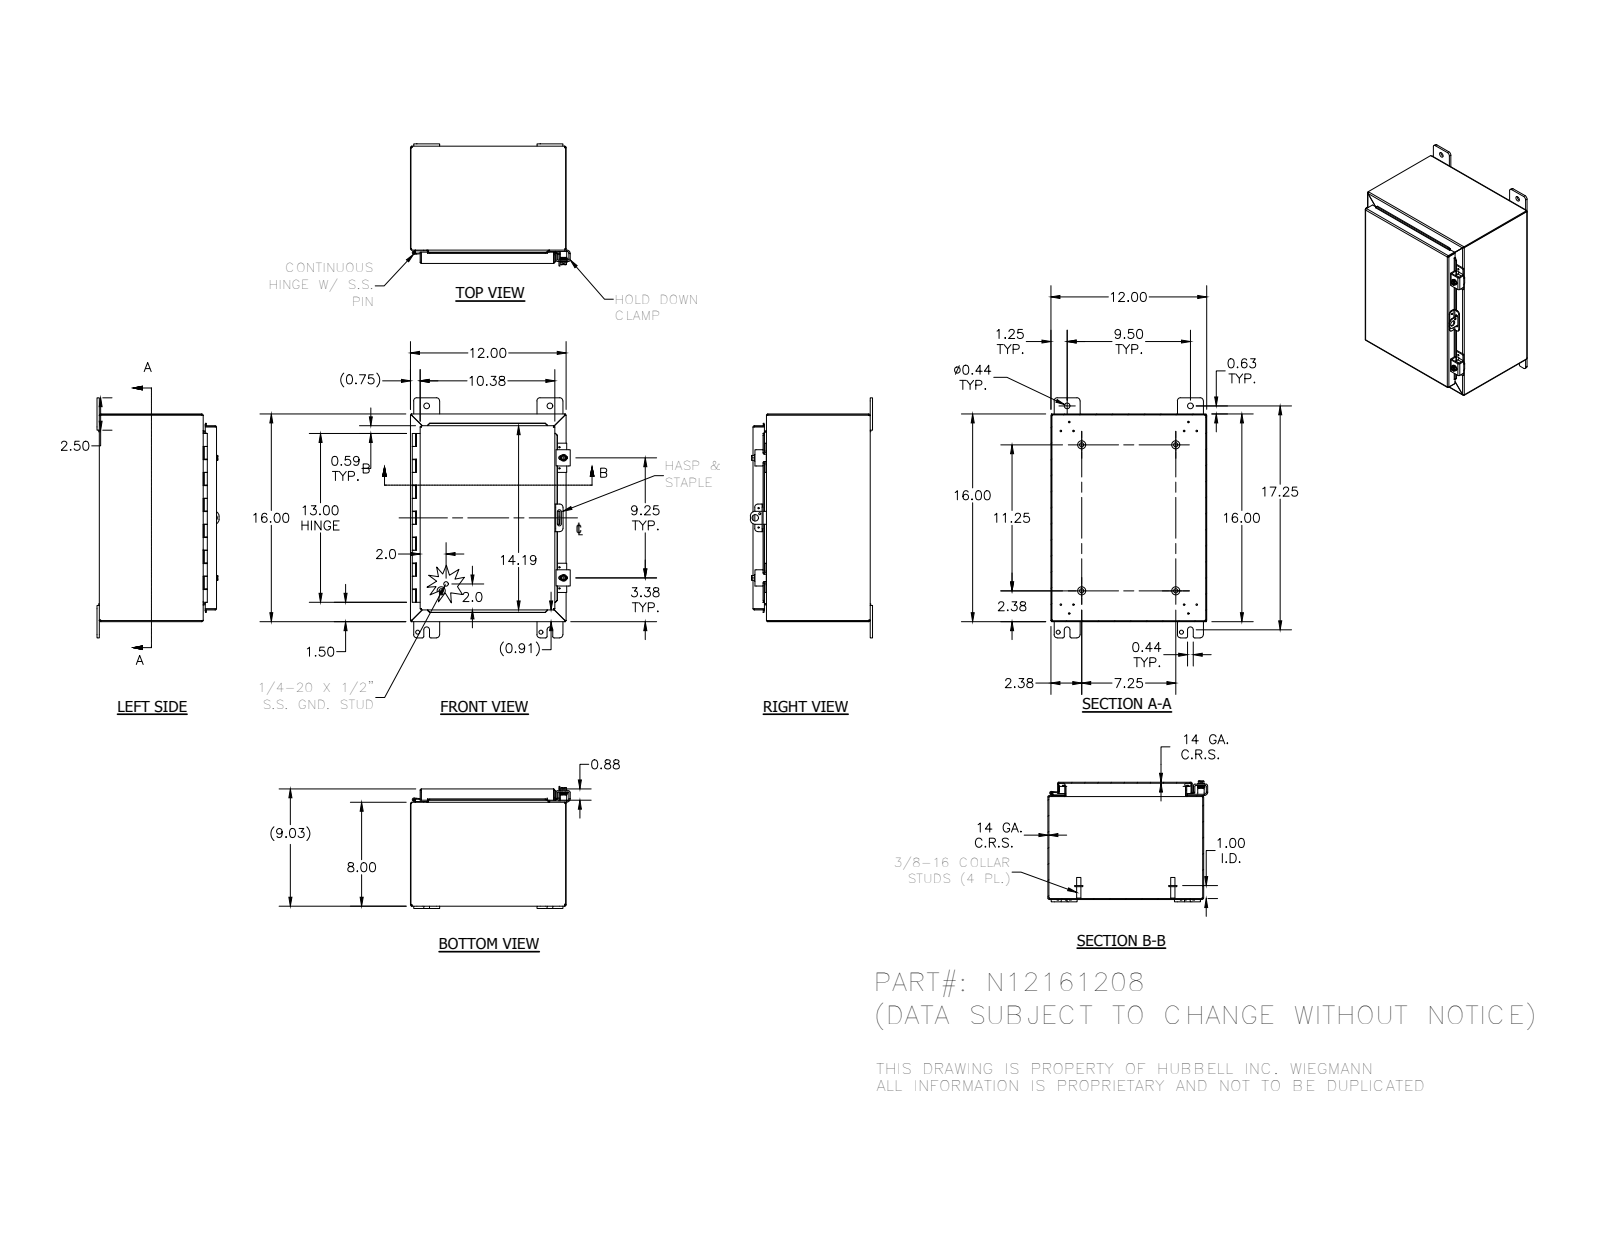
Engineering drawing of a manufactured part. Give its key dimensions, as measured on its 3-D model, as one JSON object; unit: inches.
{"part_name": "N12161208; 34840; 38420; N12161208BKP (+8 more)", "step_written_by": "Autodesk Inventor 2012 (AUTOMOTIVE_DESIGN)", "units": "inches", "bodies": {"solids": 27, "faces": 914, "planar": 489, "cylindrical": 308, "other": 117}, "overall_size": [18.5, 12.311, 9.41], "volume_in3": 80.93, "surface_area_in2": 2086, "round_holes": [[0.12, 12], [0.11, 7], [0.313, 4], [0.438, 4], [0.211, 2], [0.281, 2], [0.3, 2], [0.125, 1], [0.156, 1], [0.5, 1]], "round_bosses_or_shafts": [[0.625, 4], [0.33, 4], [0.25, 4], [0.52, 2], [0.5, 2], [0.35, 2], [0.115, 2], [0.337, 1]], "partial_cylinders_radius": [[0.03, 27], [0.063, 25], [0.125, 25], [0.25, 25], [0.031, 23], [0.105, 23], [0.07, 8], [0.1, 4]], "face_to_face_distances": [0.074, 8.959, 11.926, 15.926, 8.885, 9.033, 7.926, 1.033, 11.852, 12], "hole_center_spacings": [9.5, 0.759, 0.839, 0.94, 0.969, 1.593, 1.995, 8.883]}
